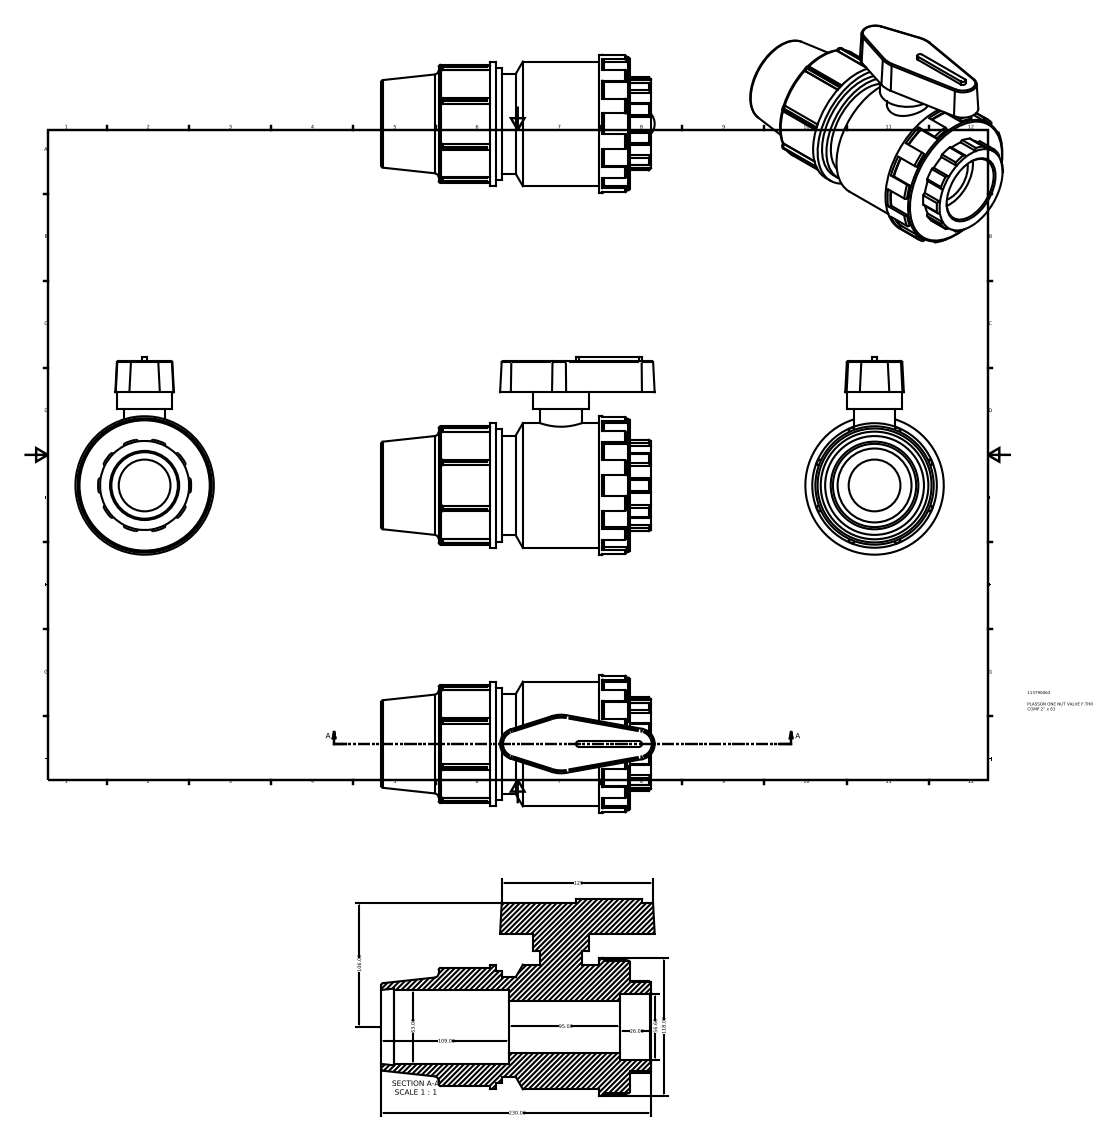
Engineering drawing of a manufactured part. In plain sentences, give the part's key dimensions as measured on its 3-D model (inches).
The part is named "113790063". Its 3-D file was written by "Autodesk Inventor 2015 (AUTOMOTIVE_DESIGN)". It is 1 solid with 248 faces: 99 planar, 74 cylindrical and 75 other. Overall it measures 9.182 by 6.621 by 4.646 inches. Its volume is 81.22 cubic inches and its surface area 236.2 square inches. Round holes: 1 of diameter 1.736, 1 of diameter 2.231, 1 of diameter 2.48. Round bosses or shafts: 1 of diameter 4.646, 1 of diameter 4.46, 1 of diameter 4.181, 1 of diameter 3.972, 1 of diameter 3.763, 1 of diameter 3.345, 1 of diameter 1.858, 1 of diameter 1.394. Partial cylindrical surfaces (rounded edges, fillets, slot ends): 20 of radius 0.067, 16 of radius 0.074, 4 of radius 0.044, 2 of radius 0.093, 1 of radius 1.494, 1 of radius 1.561. The main face-to-face distances are 1.024, 1.043, 0.717, 1.74, 3.453, 4.476, 5.193, 1.931, 0.429, 3.024.
